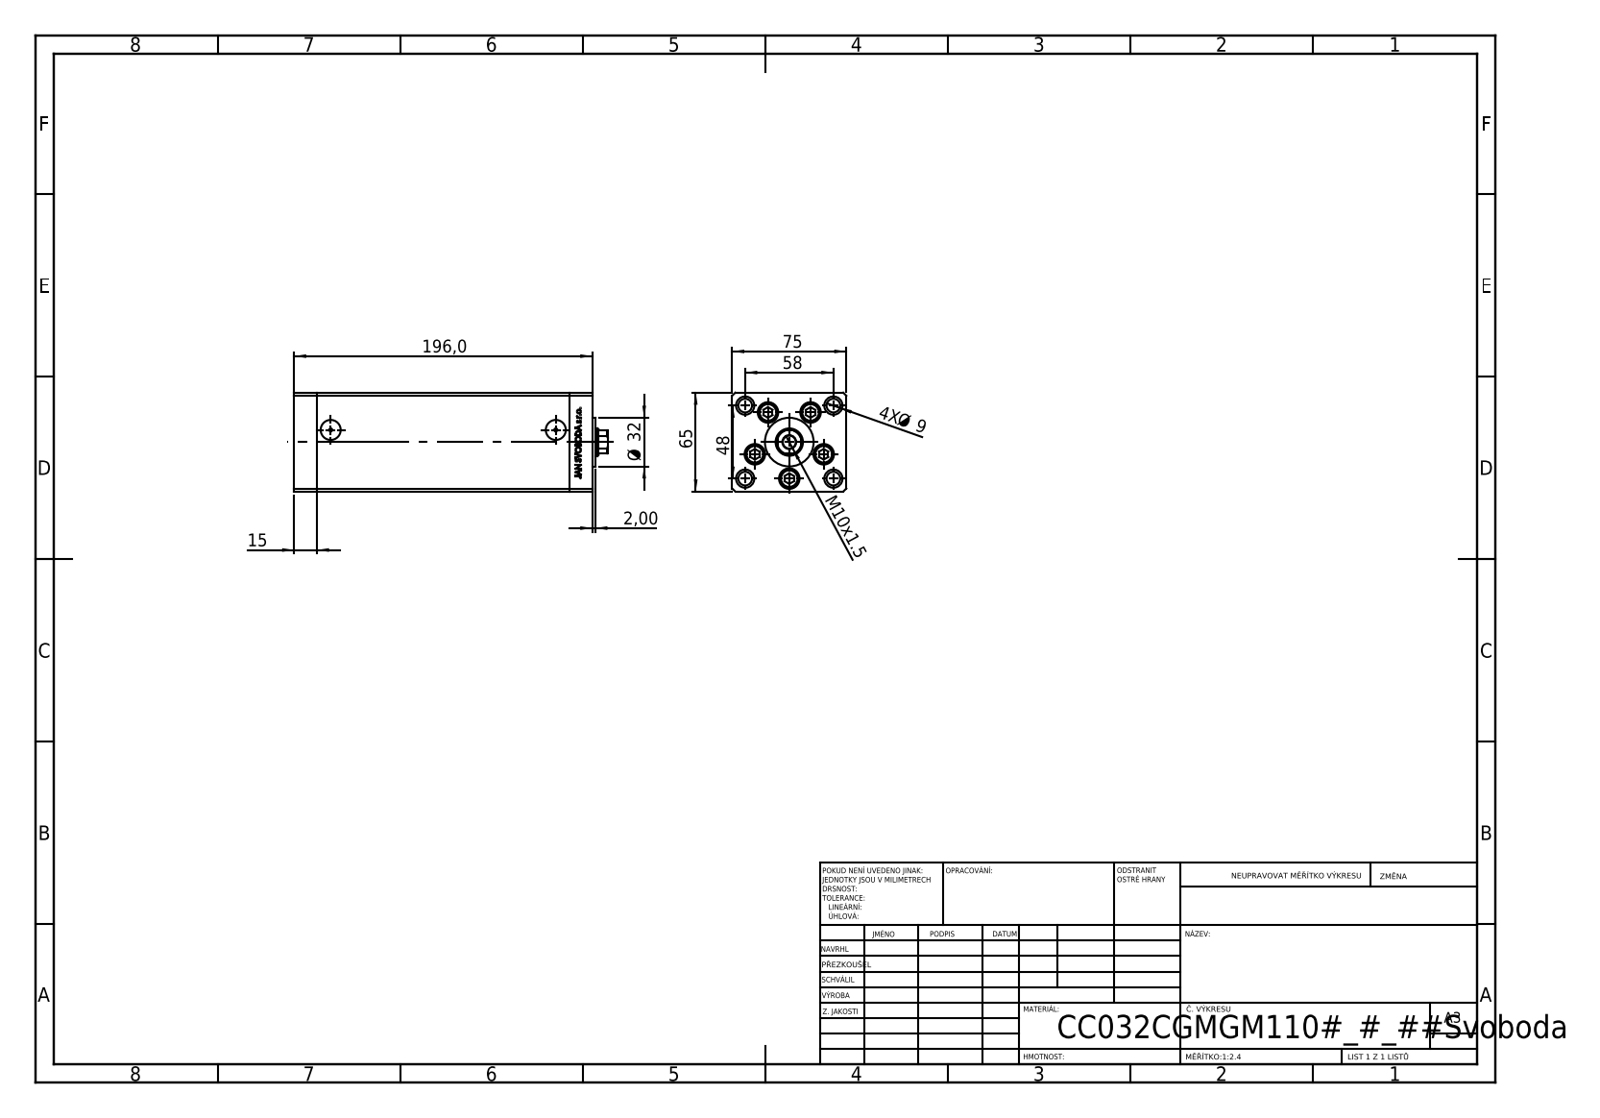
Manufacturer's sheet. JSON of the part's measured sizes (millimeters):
{"part_name": "ALLEN BOLT; V220C_VC_C; V220C FRONT; V220C_C MIDDLE (+1 more)", "step_written_by": "SolidWorks 2019 (CONFIG_CONTROL_DESIGN)", "units": "millimeters", "bodies": {"solids": 13, "faces": 1173, "planar": 544, "cylindrical": 167, "other": 462}, "overall_size": [206, 75, 65], "volume_mm3": 797094, "surface_area_mm2": 159893, "round_holes": [[9, 9], [13.5, 5], [8, 4], [12, 4], [2, 2], [13.16, 2], [8.5, 1], [12.5, 1], [18, 1]], "round_bosses_or_shafts": [[8, 5], [12.5, 4], [32, 1]], "partial_cylinders_radius": [[0.93, 2], [8.5, 1]], "face_to_face_distances": [75, 65, 15, 166, 181, 196, 54.5, 10.5, 28, 26.25], "hole_center_spacings": [24, 37.64, 15.67, 17.22, 27.71, 28.83, 29, 32.63]}
